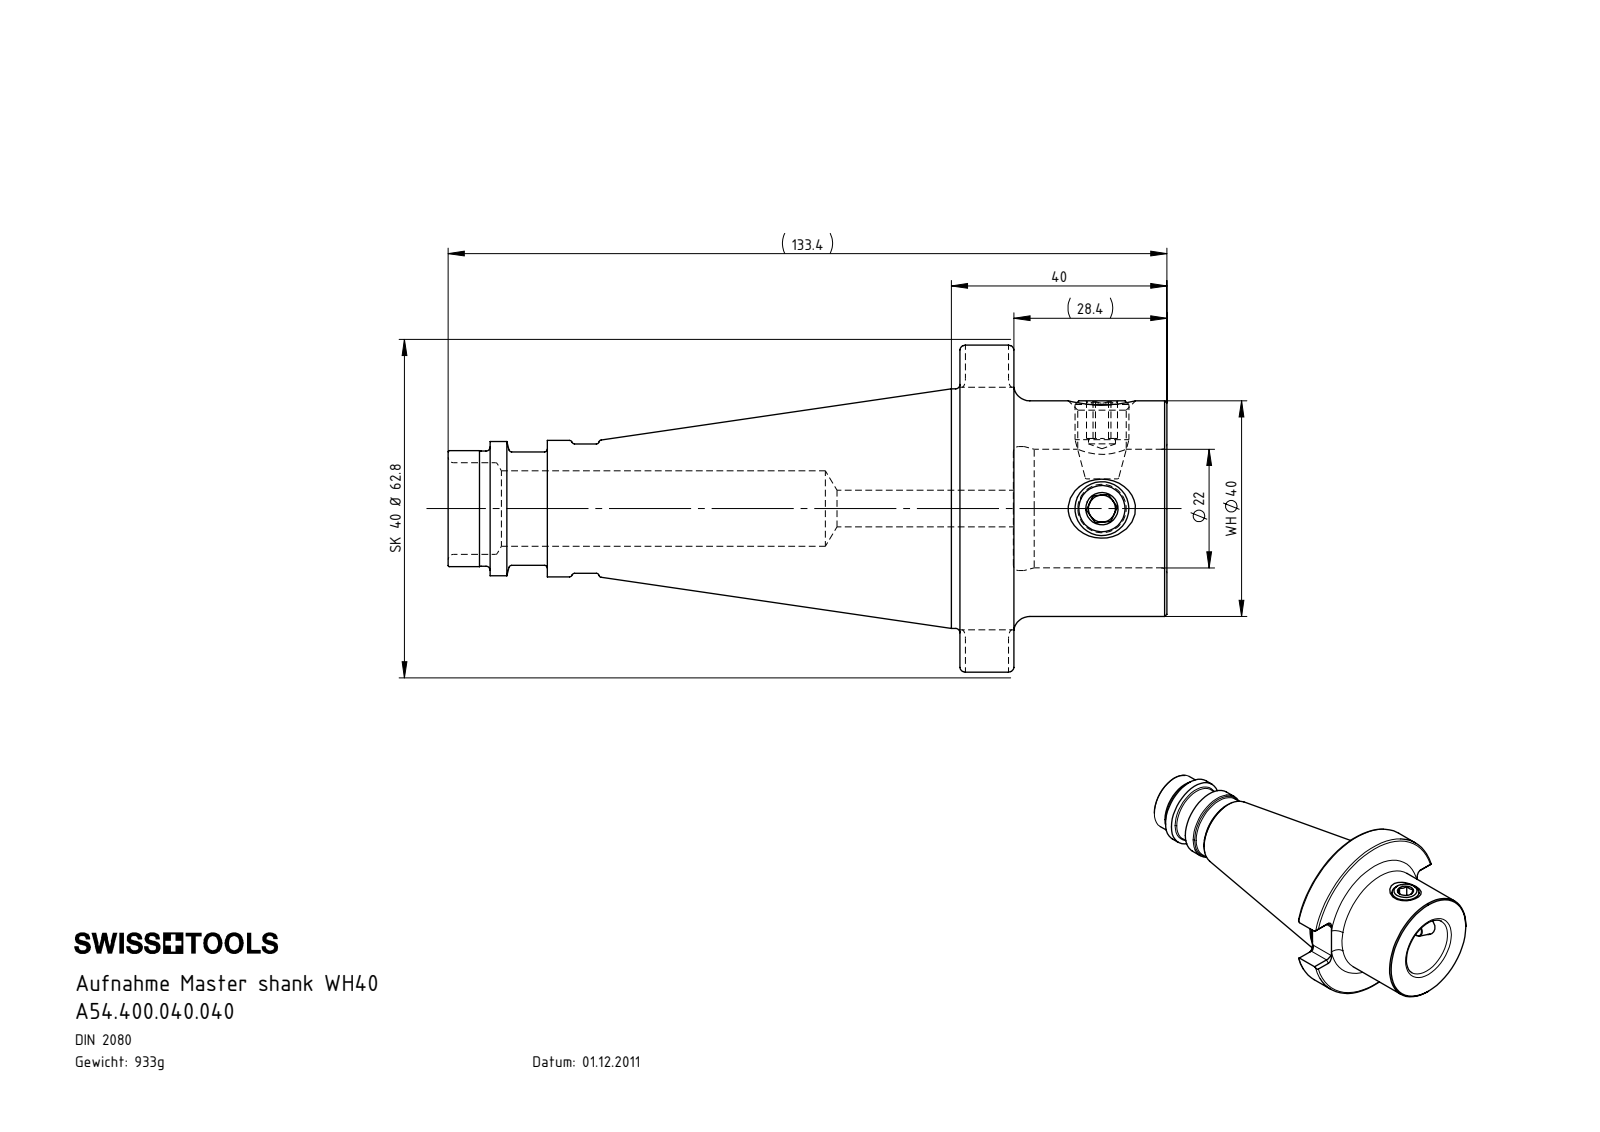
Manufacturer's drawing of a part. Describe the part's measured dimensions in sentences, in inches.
The part is named "SZ4-WH4.K01.040_B; A54.400.040.040; WH4-ER1.001.015". Its 3-D file was written by "SolidWorks 2022 (CONFIG_CONTROL_DESIGN)". It is 3 solids with 179 faces: 53 planar, 52 cylindrical and 74 other. Overall it measures 5.252 by 2.472 by 2.39 inches. Its volume is 7.253 cubic inches and its surface area 41.9 square inches. Round holes: 2 of diameter 0.197, 2 of diameter 0.354, 1 of diameter 0.268, 1 of diameter 0.551, 1 of diameter 0.669, 1 of diameter 0.866, 1 of diameter 0.906. Round bosses or shafts: 2 of diameter 0.394, 1 of diameter 2.472, 1 of diameter 1.75, 1 of diameter 1.575, 1 of diameter 0.996, 1 of diameter 0.981, 1 of diameter 0.945, 1 of diameter 0.846. Partial cylindrical surfaces (rounded edges, fillets, slot ends): 12 of radius 0.063. The main face-to-face distances are 0.394, 1.512, 1.118, 0.39, 1.122, 1.772, 3.016, 3.406, 3.409, 4.528.
